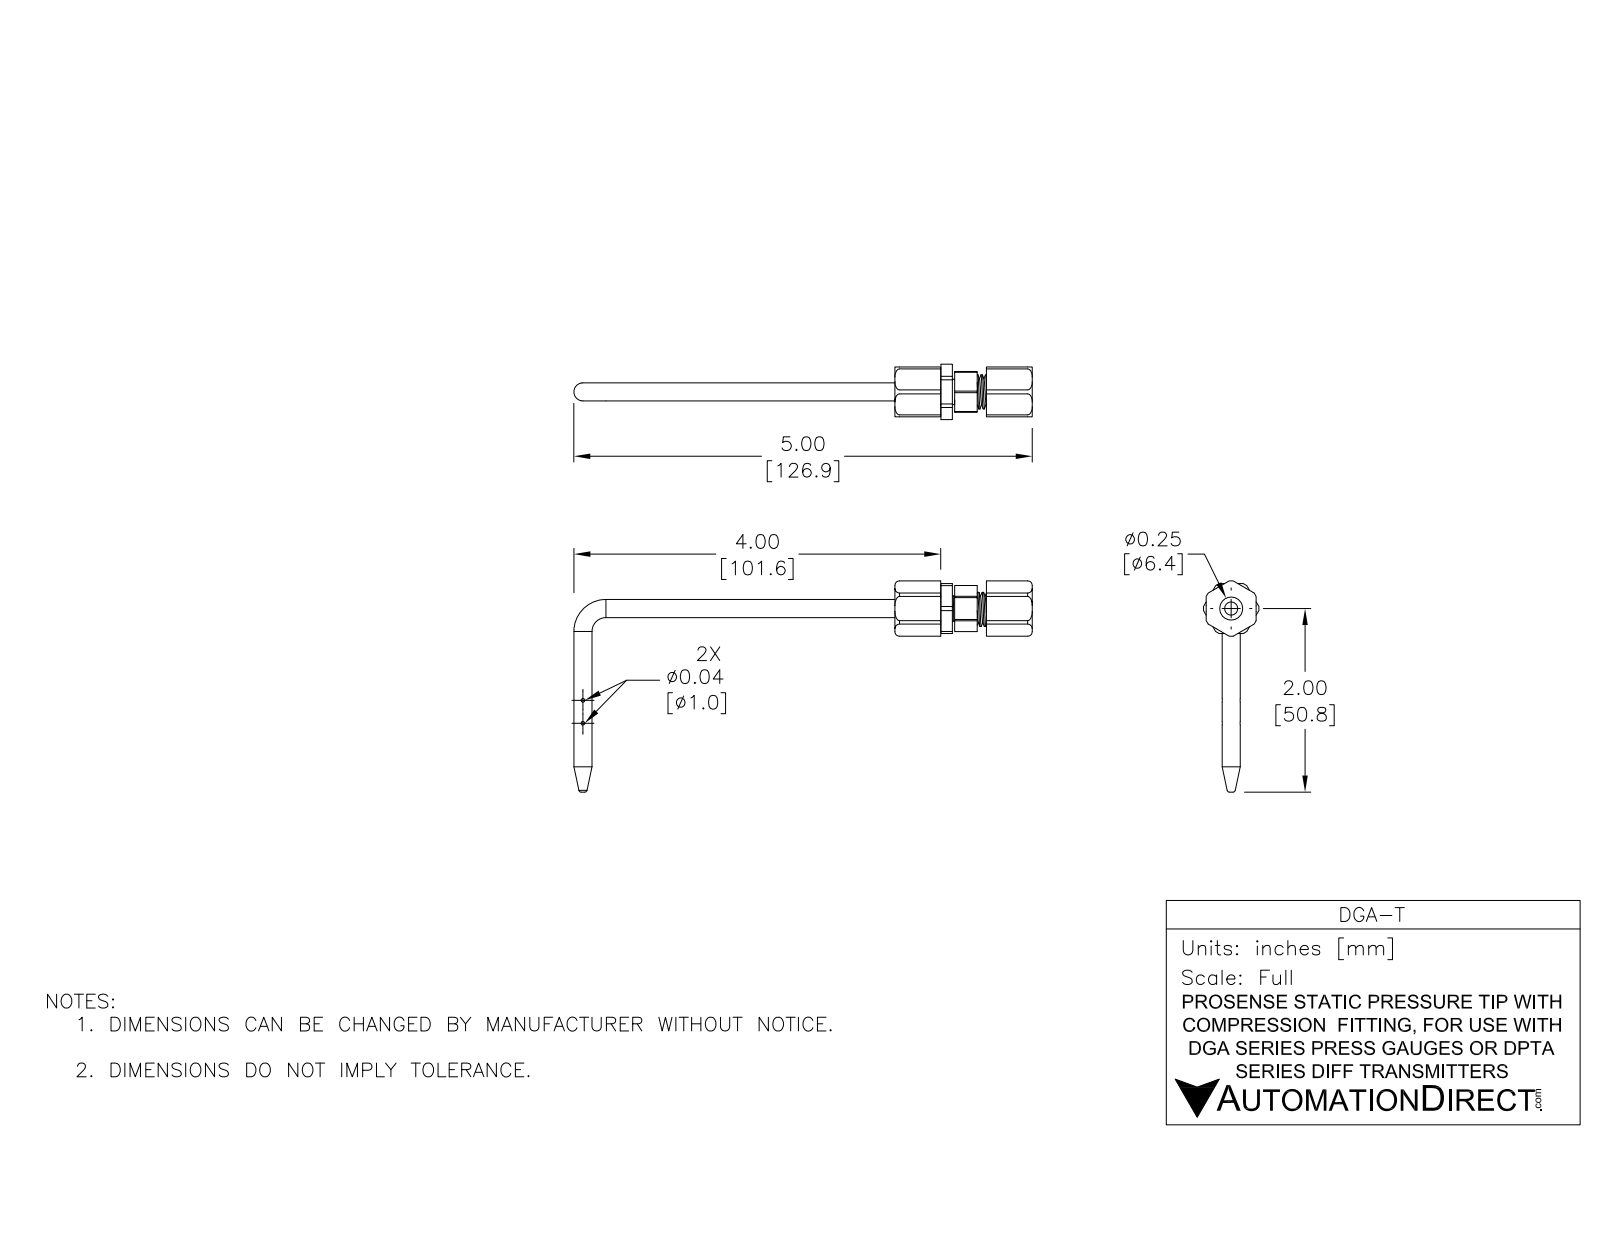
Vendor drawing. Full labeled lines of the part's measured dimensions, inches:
Part name (STEP PRODUCT): DGA-T
STEP written by: SolidWorks 2017 (AUTOMOTIVE_DESIGN)
Units: inches
Bodies: 2 solids, 118 faces (61 planar, 36 cylindrical, 21 other)
Overall size (bounding box): 4.846 × 2.301 × 0.603
Volume: 0.361 in³ · Surface area: 11.25 in²
Round holes (diameter × count): ⌀0.04 ×2, ⌀0.142 ×2, ⌀0.25 ×1
Round bosses / shafts (diameter × count): ⌀0.197 ×2, ⌀0.275 ×1
Partial cylindrical surfaces — rounded edges, fillets, slot ends (radius × count): R0.05 ×12
Main face-to-face distances: 0.544, 0.05, 0.5, 0.998, 0.494, 0.03, 0.574, 0.37, 0.498, 0.127
Hole centre spacings: 0.25
